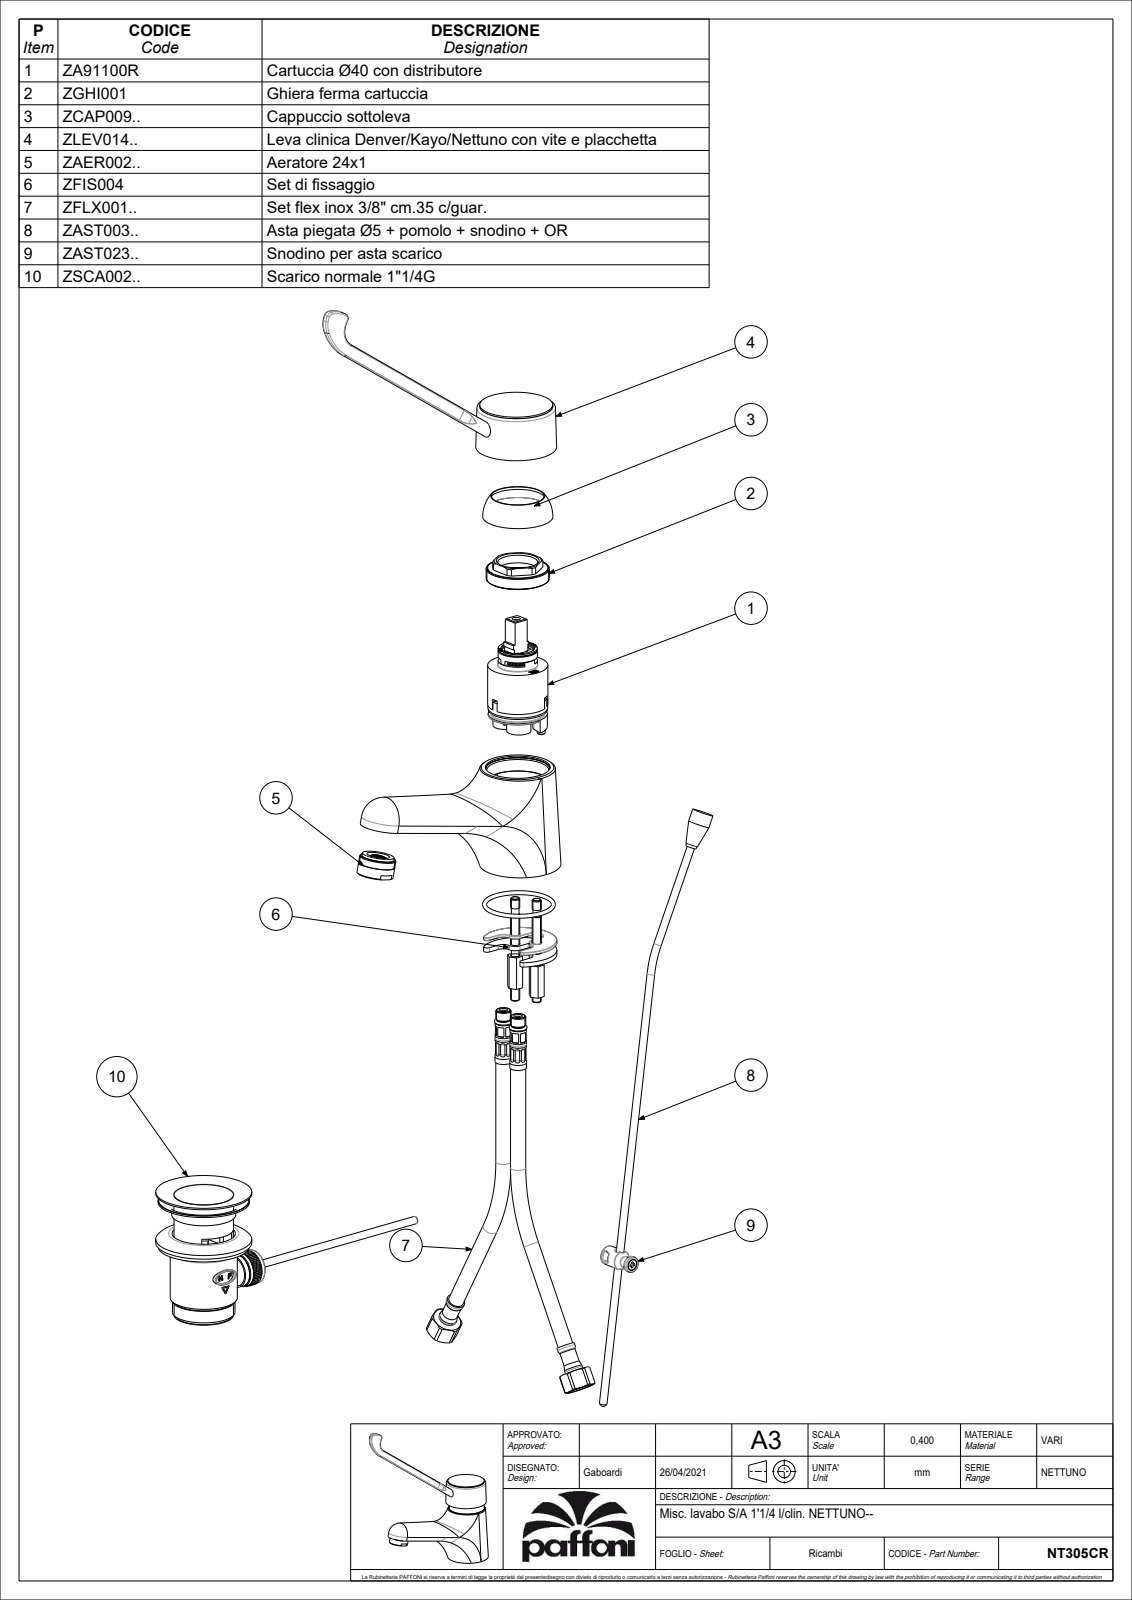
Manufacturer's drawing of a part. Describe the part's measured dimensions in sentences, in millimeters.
The part is named "NT305CR". Its 3-D file was written by "CREO PARAMETRIC BY PTC INC, 2020044 (CONFIG_CONTROL_DESIGN)". It is 3 solids with 2871 faces: 2117 planar, 423 cylindrical and 331 other. Overall it measures 216.93 by 208.58 by 53.5 millimeters. Its volume is 161 588 cubic millimeters and its surface area 103 439 square millimeters. Round holes: 4 of diameter 8, 3 of diameter 5.5, 3 of diameter 11, 2 of diameter 4.6, 2 of diameter 7, 2 of diameter 9, 2 of diameter 12, 2 of diameter 21, 1 of diameter 3.3, 1 of diameter 4, 1 of diameter 4.3, 1 of diameter 5. Round bosses or shafts: 3 of diameter 5, 2 of diameter 15.9, 2 of diameter 10, 2 of diameter 9.4, 2 of diameter 8.2, 2 of diameter 6, 1 of diameter 47.85, 1 of diameter 39.5. Partial cylindrical surfaces (rounded edges, fillets, slot ends): 69 of radius 0.5, 24 of radius 0.2, 8 of radius 0.3, 6 of radius 1.5, 4 of radius 7.5, 2 of radius 2, 2 of radius 5.5, 2 of radius 6.5. The main face-to-face distances are 3.5, 6, 4.5, 1.5, 3, 0.5, 4, 10, 22, 38.1. The hole center spacings are 1.12, 13.04, 14.53, 2, 8.6, 9.6, 9.9, 11.05.
